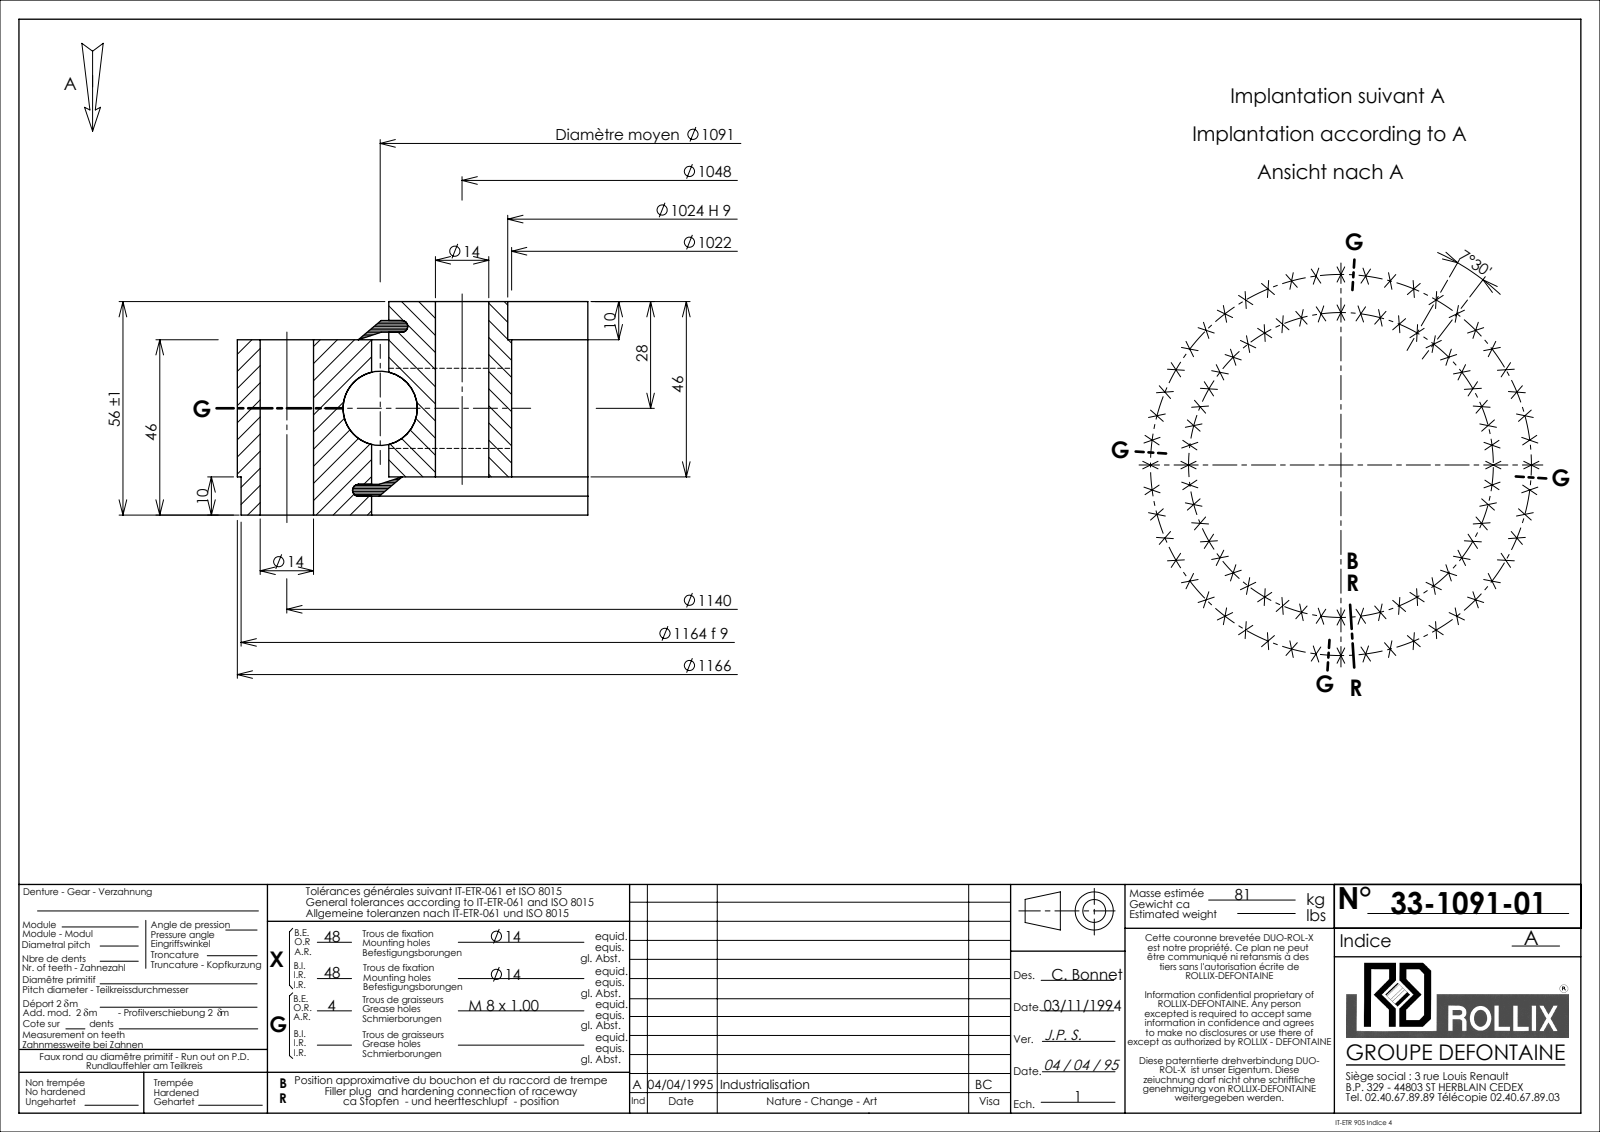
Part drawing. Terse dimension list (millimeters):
name: 33-1091-01
written by: SolidWorks 2016 (CONFIG_CONTROL_DESIGN)
unit: mm
bodies: 9 solids, 350 faces (54 planar, 228 cylindrical, 68 other)
size: 1183.07 × 1183.07 × 56
volume: 9 308 000 mm³; area: 1 579 000 mm²
holes: 96× ⌀14, 4× ⌀7, 1× ⌀1022, 1× ⌀1024, 1× ⌀1095.5
bosses: 4× ⌀8, 1× ⌀1166, 1× ⌀1164, 1× ⌀1086.5
face distances: 46, 10, 36, 56, 8.05, 47.95, 1.95, 37.95, 4.95, 51.05
hole spacings: 463.52, 68.54, 271.24, 136.79, 204.46, 336.87, 741.05, 582.24
